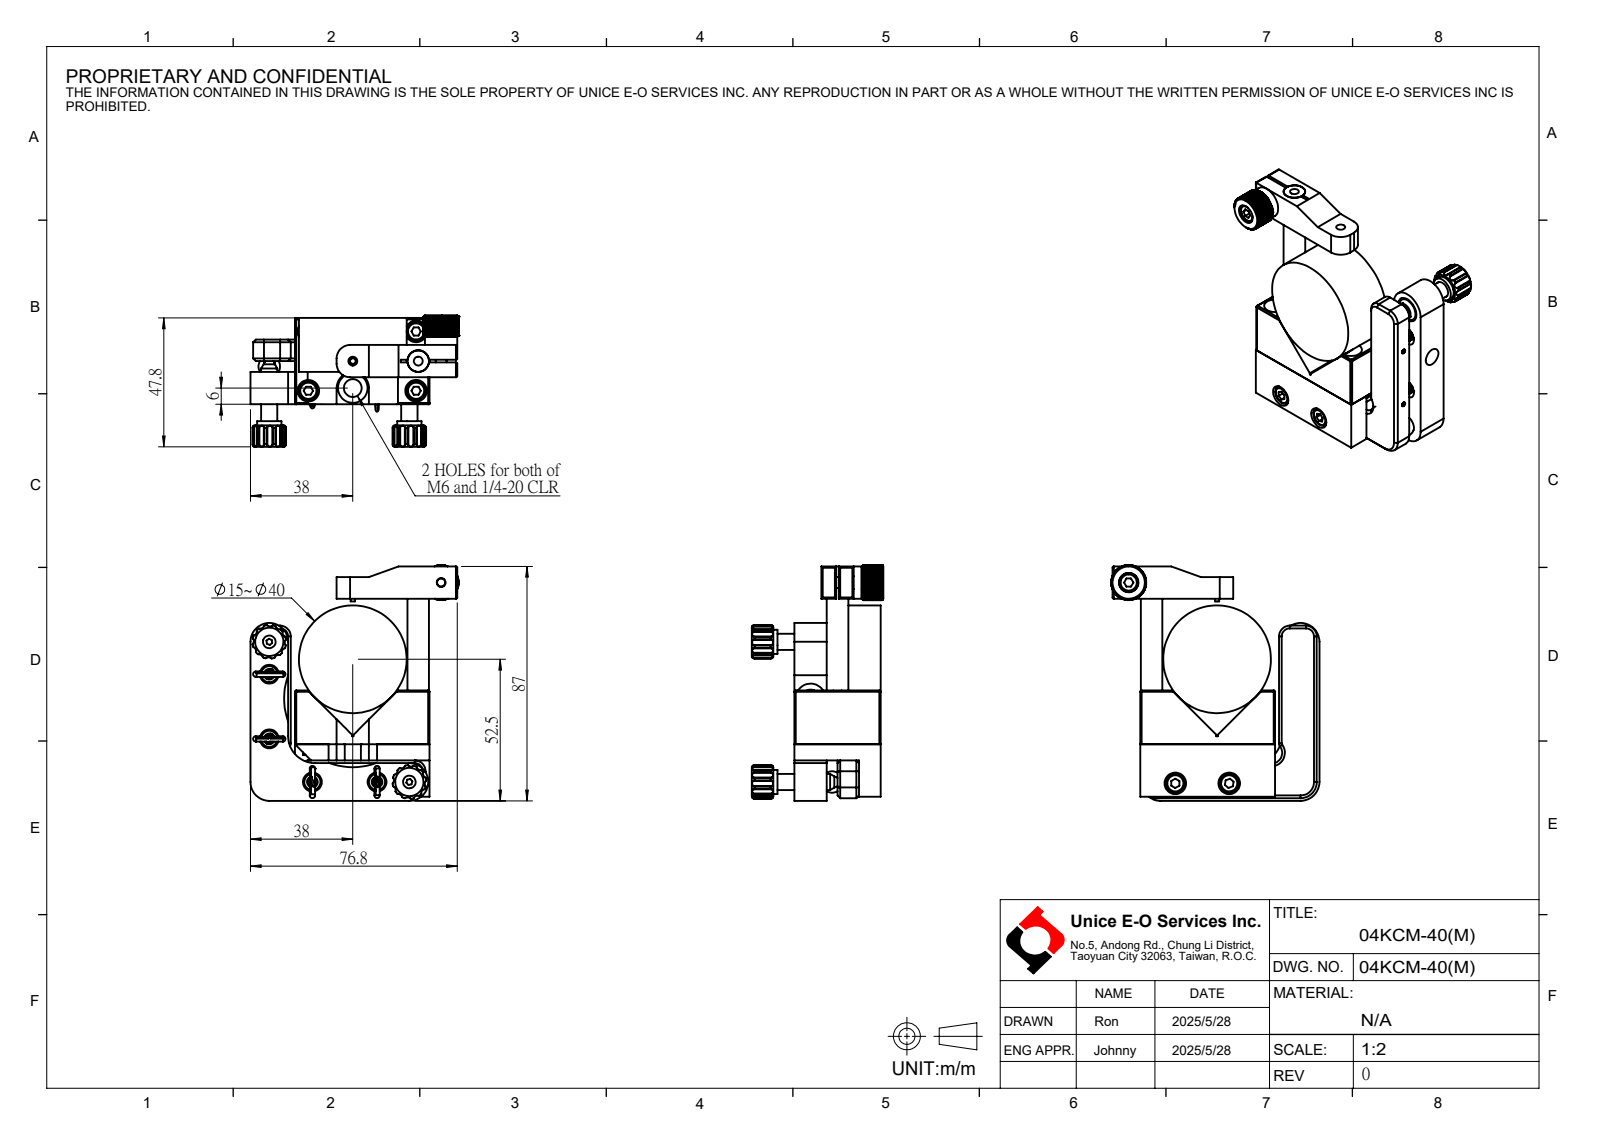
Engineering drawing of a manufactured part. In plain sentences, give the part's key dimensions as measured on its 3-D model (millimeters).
The part is named "04KCM-40(M)". Its 3-D file was written by "SolidWorks 2024 (CONFIG_CONTROL_DESIGN)". It is 0 solids with 666 faces: 150 planar, 438 cylindrical and 78 other. Overall it measures 87.5 by 77.3 by 48.81 millimeters. Round holes: 7 of diameter 3.3, 6 of diameter 1.1, 6 of diameter 8, 4 of diameter 1.7, 4 of diameter 7, 2 of diameter 4.7, 2 of diameter 6.6, 2 of diameter 9.5, 2 of diameter 11, 1 of diameter 7.2. Round bosses or shafts: 10 of diameter 1.5, 2 of diameter 9, 2 of diameter 6, 2 of diameter 0.8, 1 of diameter 40, 1 of diameter 12, 1 of diameter 8, 1 of diameter 7. Partial cylindrical surfaces (rounded edges, fillets, slot ends): 72 of radius 0.1, 48 of radius 0.3, 25 of radius 1.5, 14 of radius 0.5, 8 of radius 1, 5 of radius 4, 4 of radius 0.75, 4 of radius 3. The main face-to-face distances are 12, 8, 20, 16, 32, 6, 24, 14, 10, 1. The hole center spacings are 24, 11.03, 12, 16.64, 18.25, 19.83, 20.52, 22.
